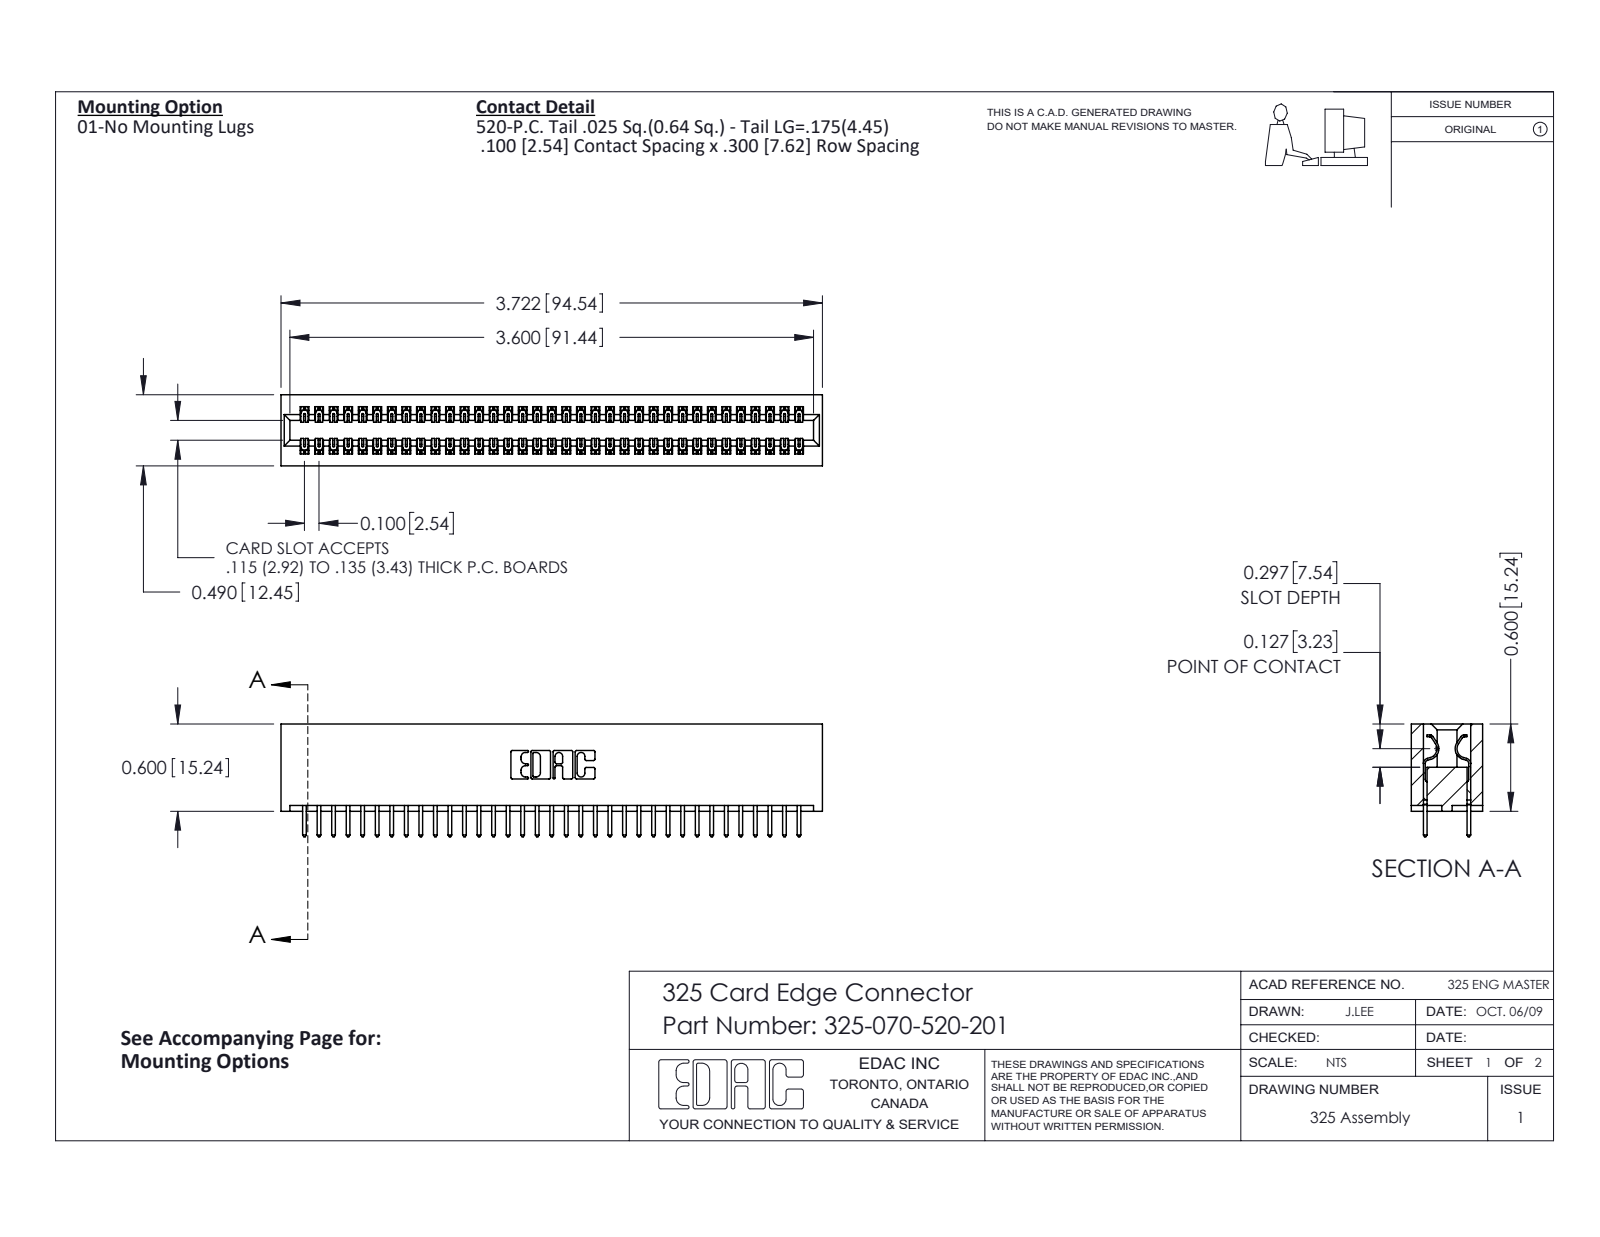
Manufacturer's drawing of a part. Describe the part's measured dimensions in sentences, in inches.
The part is named "325-070-520-201; 325-292-001_325-293-120; 325 Part_Lugless". Its 3-D file was written by "SolidWorks 2016 (CONFIG_CONTROL_DESIGN)". It is 71 solids with 3746 faces: 2586 planar, 1160 cylindrical and 0 other. Overall it measures 3.722 by 0.775 by 0.49 inches. Its volume is 0.777 cubic inches and its surface area 24.44 square inches. Partial cylindrical surfaces (rounded edges, fillets, slot ends): 105 of radius 0.006, 70 of radius 0.01, 22 of radius 0.01, 6 of radius 0.007, 6 of radius 0.031, 3 of radius 0.026, 2 of radius 0.014, 2 of radius 0.022. The main face-to-face distances are 0.083, 0.407, 0.3, 0.49, 0.107, 0.383, 0.025, 0.325, 0.275, 0.56.
